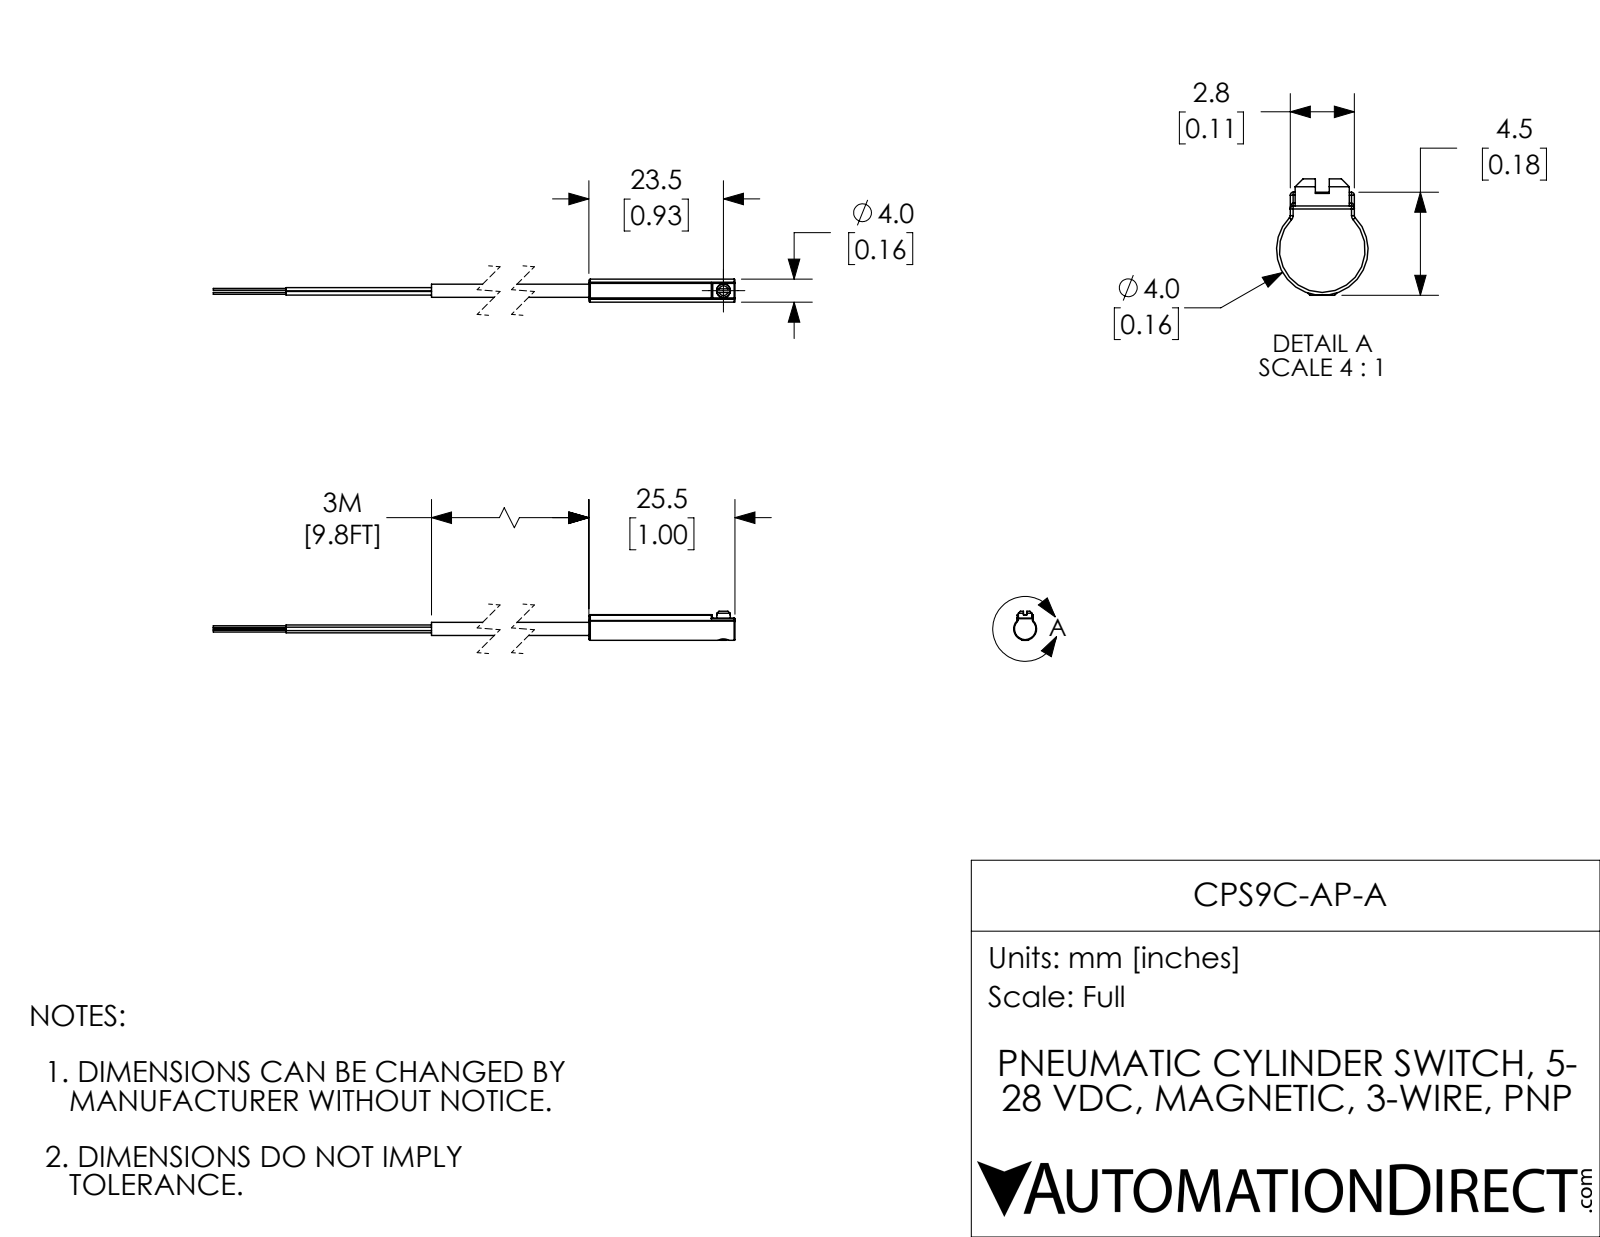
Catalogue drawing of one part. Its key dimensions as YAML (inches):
part_name: "CPS9C-AP-A"
step_written_by: "SolidWorks 2019 (AUTOMOTIVE_DESIGN)"
units: inches
bodies: {solids: 2, faces: 84, planar: 20, cylindrical: 37, other: 27}
overall_size: [6.689, 0.2, 0.157]
volume: 0.051
surface_area: 2.16
round_holes:
  - {diameter: 0.076, count: 1}
round_bosses_or_shafts:
  - {diameter: 0.024, count: 3}
  - {diameter: 0.013, count: 3}
  - {diameter: 0.093, count: 1}
  - {diameter: 0.09, count: 1}
partial_cylinders:
  - {radius: 0.005, count: 13}
  - {radius: 0.01, count: 3}
  - {radius: 0.079, count: 1}
face_to_face_distances: [0.11, 1.004, 0.024, 5.189, 4.185, 0.043, 0.067, 0.022, 0.046, 0.025]
